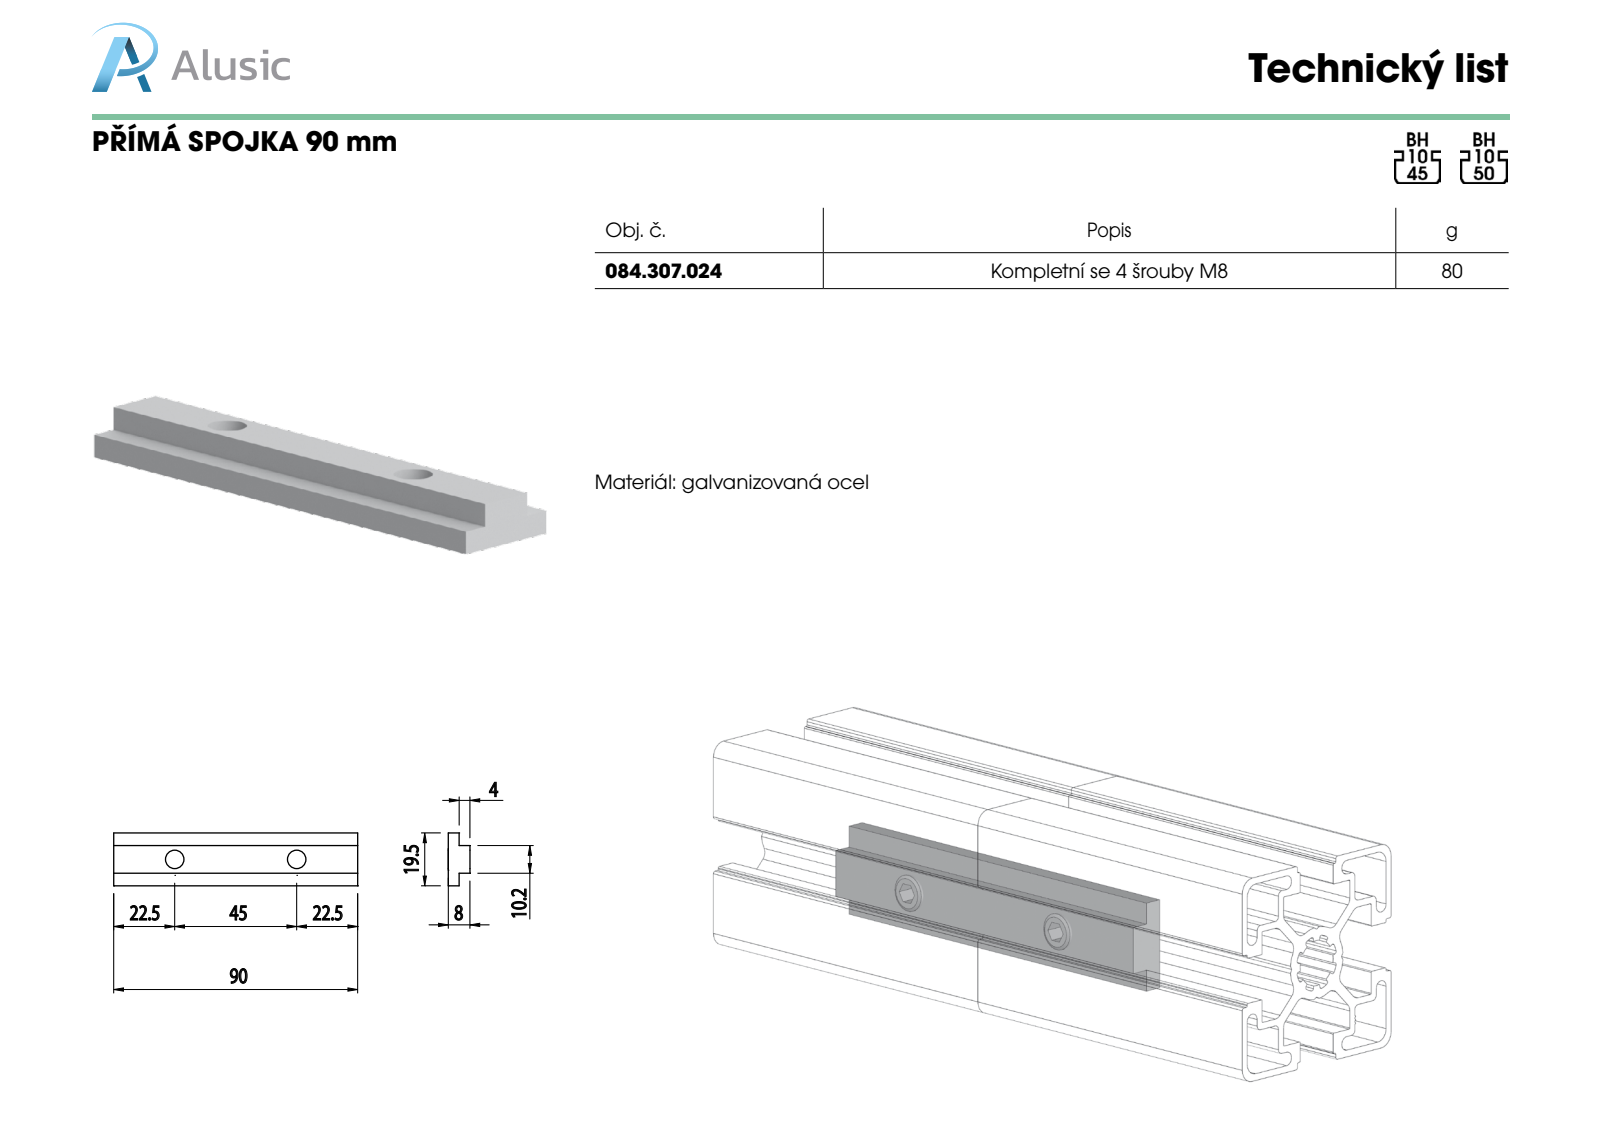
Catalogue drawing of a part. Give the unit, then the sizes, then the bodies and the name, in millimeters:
Units: millimetres
Overall size (bounding box): 90 × 19.5 × 8
Round holes (diameter × count): ⌀6.8 ×2
Main face-to-face distances: 4, 8, 4.65, 14.85, 19.5, 10.2, 90
Hole centre spacings: 45
Volume: 10 111 mm³ · Surface area: 5 384 mm²
Bodies: 1 solid, 14 faces (10 planar, 4 cylindrical, 0 other)
Part name (STEP PRODUCT): 084.307.024
STEP written by: SolidWorks 2011 (CONFIG_CONTROL_DESIGN)
